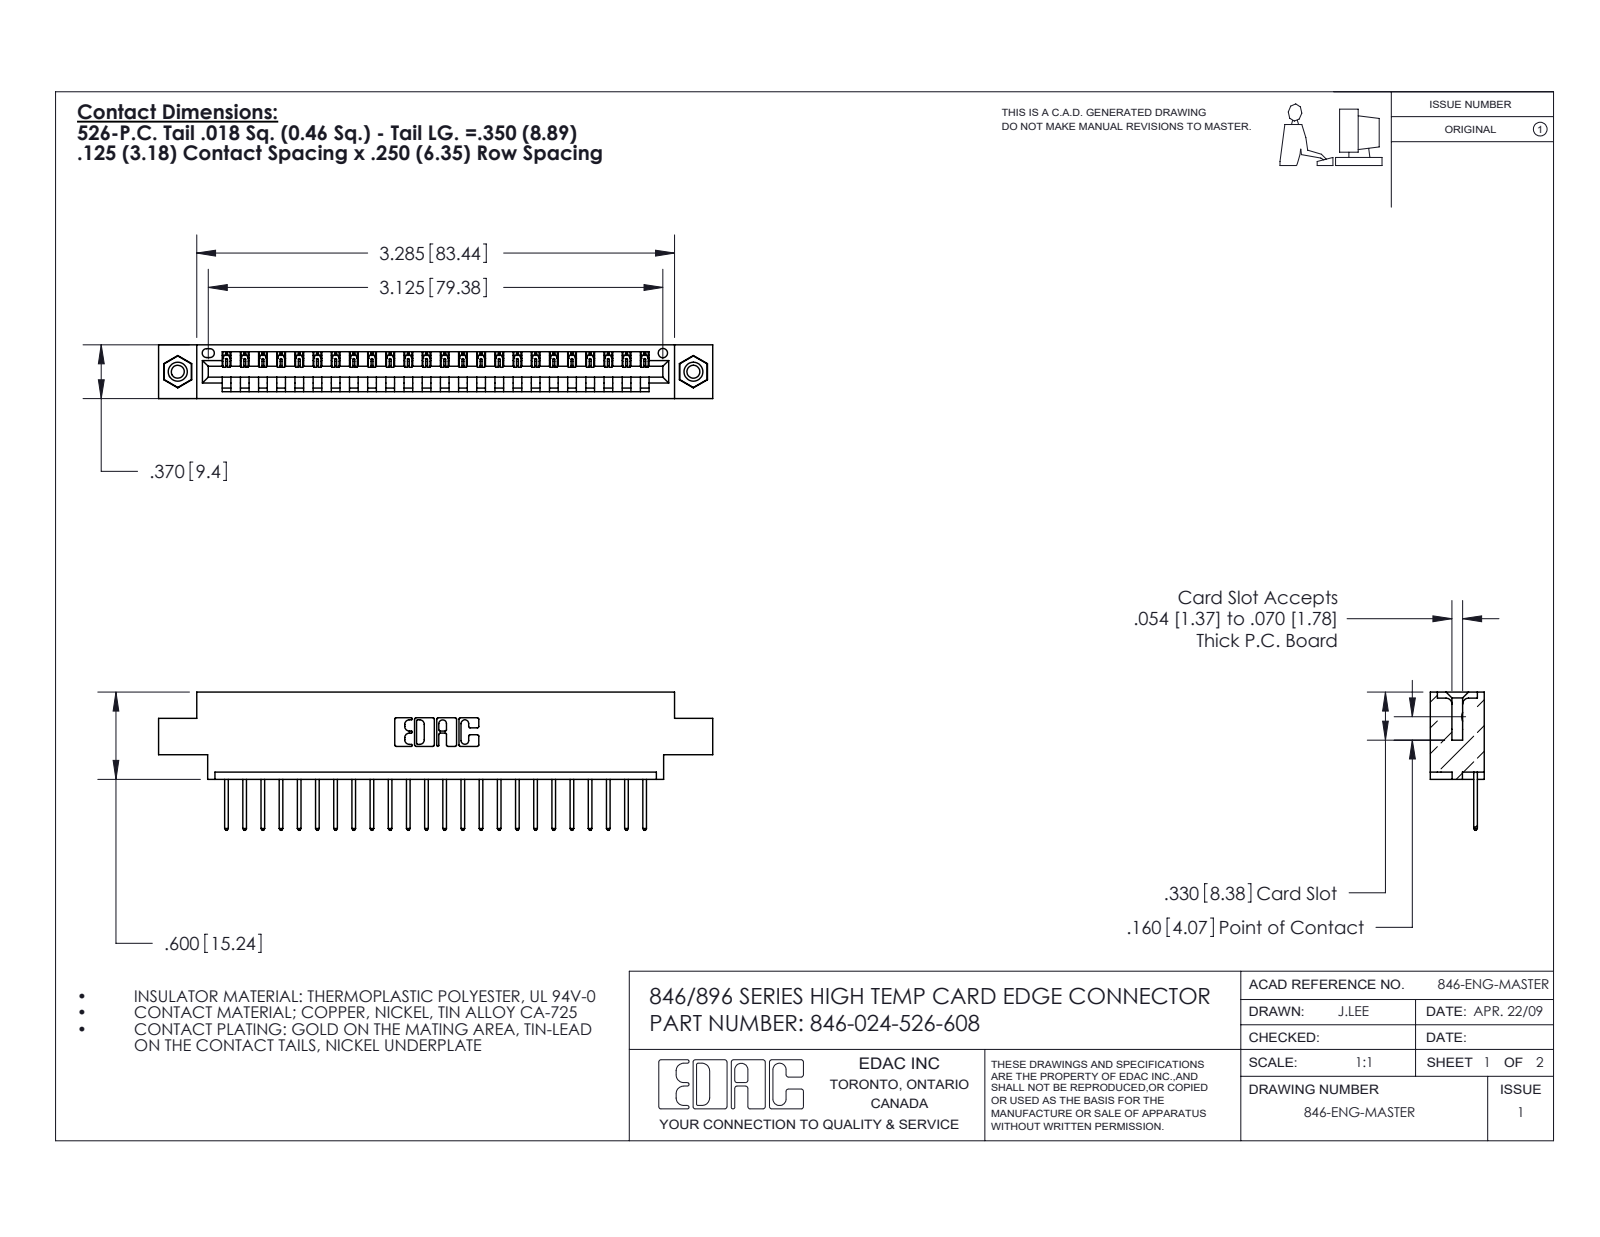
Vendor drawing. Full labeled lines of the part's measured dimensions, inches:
Part name (STEP PRODUCT): 346-024-526-608; 345-250-001_345-250-003-102; 346 Part_0.170 Offset - 0.156 Dia-TI; 345-292-001_345-293-126
STEP written by: SolidWorks 2016 (CONFIG_CONTROL_DESIGN)
Units: inches
Bodies: 27 solids, 1578 faces (1072 planar, 490 cylindrical, 16 other)
Overall size (bounding box): 3.81 × 0.95 × 0.37
Volume: 0.547 in³ · Surface area: 17.3 in²
Round holes (diameter × count): ⌀0.089 ×2, ⌀0.125 ×2, ⌀0.156 ×2, ⌀0.064 ×1
Round bosses / shafts (diameter × count): ⌀0.155 ×2
Partial cylindrical surfaces — rounded edges, fillets, slot ends (radius × count): R0.006 ×48, R0.01 ×48, R0.01 ×22, R0.007 ×6, R0.031 ×6, R0.026 ×3, R0.031 ×2, R0.04 ×2
Main face-to-face distances: 0.048, 0.322, 0.37, 0.25, 0.072, 0.298, 0.025, 0.222, 0.148, 0.1
Hole centre spacings: 0.246, 3.337, 3.545
